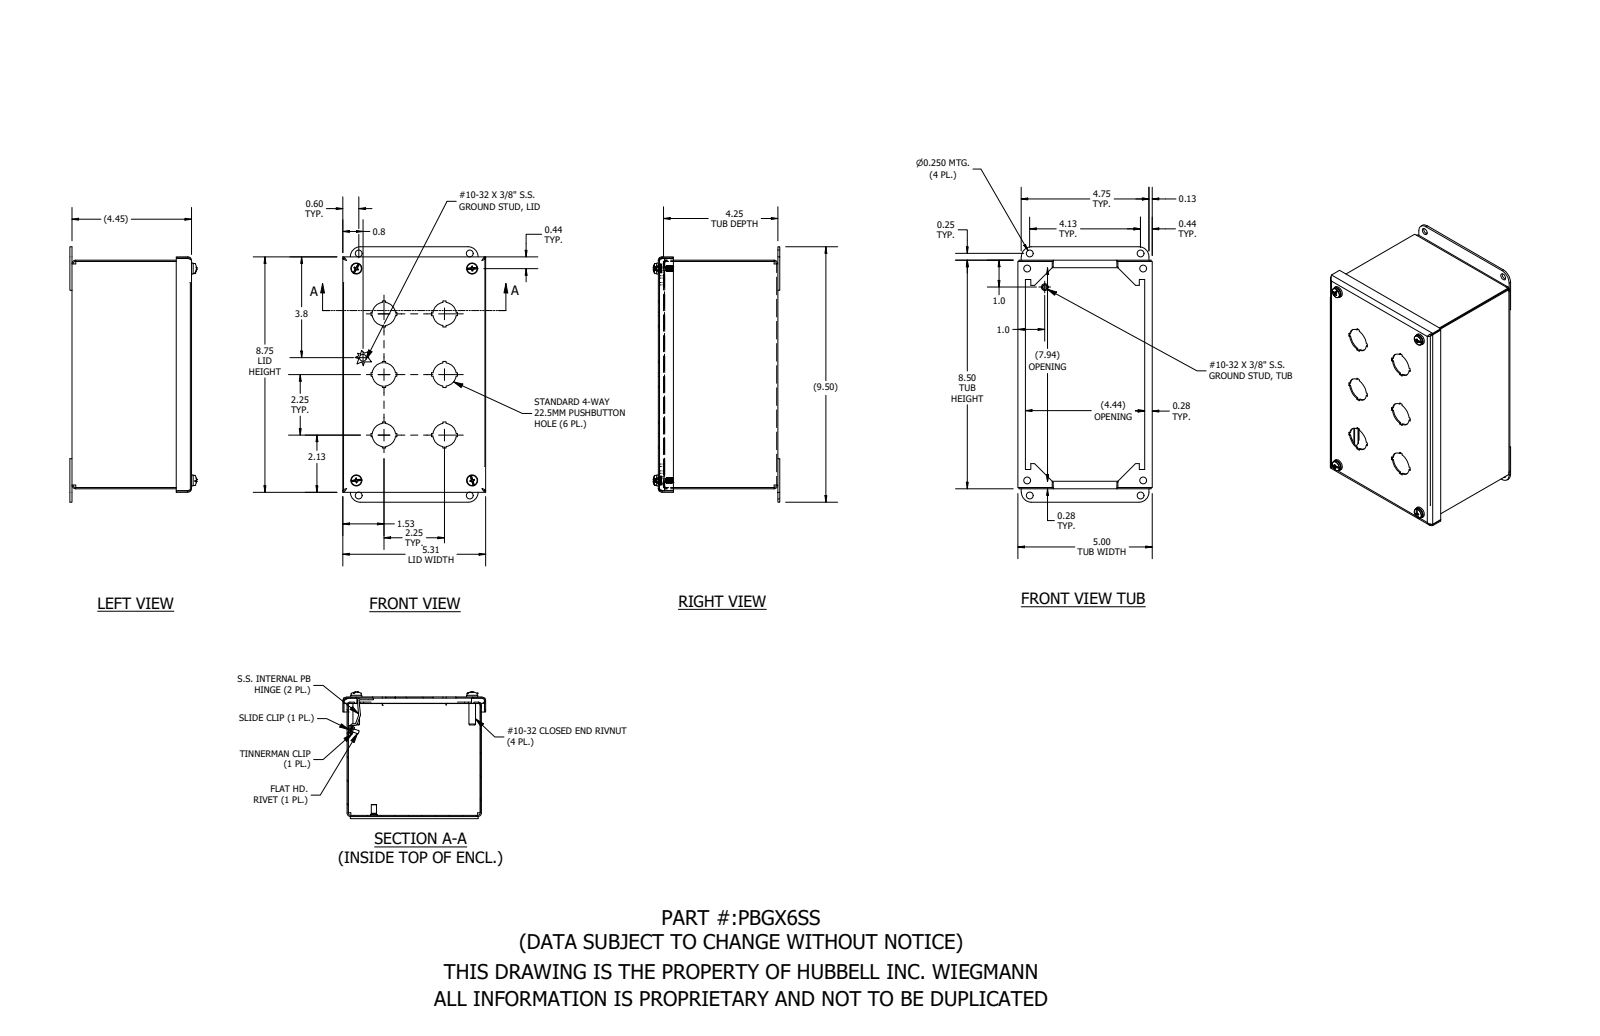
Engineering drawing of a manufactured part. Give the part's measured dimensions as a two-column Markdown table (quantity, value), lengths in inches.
| quantity | value |
| --- | --- |
| part name | PBGX6SS |
| STEP written by | SolidWorks 2021 (AUTOMOTIVE_DESIGN) |
| units | inches |
| bodies | 25 solids, 928 faces (463 planar, 313 cylindrical, 152 other) |
| overall size | 9.5 × 5.313 × 4.704 |
| volume | 14.12 in³ |
| surface area | 529.9 in² |
| round holes (diameter × count) | 0.875 × 6, 0.156 × 4, 0.196 × 4, 0.25 × 4, 0.257 × 4, 0.281 × 4, 0.313 × 4, 0.133 × 2, 0.14 × 2, 0.175 × 2, 0.175 × 2 |
| round bosses / shafts (diameter × count) | 0.406 × 4, 0.318 × 4, 0.248 × 4, 0.186 × 4, 0.141 × 4, 0.14 × 4, 0.375 × 3, 0.25 × 3 |
| partial cylindrical surfaces (radius × count) | 0.094 × 8, 0.139 × 8, 0.188 × 6, 0.063 × 4, 0.09 × 4, 0.108 × 4, 0.375 × 4, 0.031 × 3 |
| main face-to-face distances | 0.045, 4.4, 0.045, 8.455, 4.445, 4.355, 4.91, 4.955, 4.955, 5 |
| hole center spacings | 2.25, 0.019, 1.978, 3.182, 3.69, 4.07, 5.125, 6.273 |
